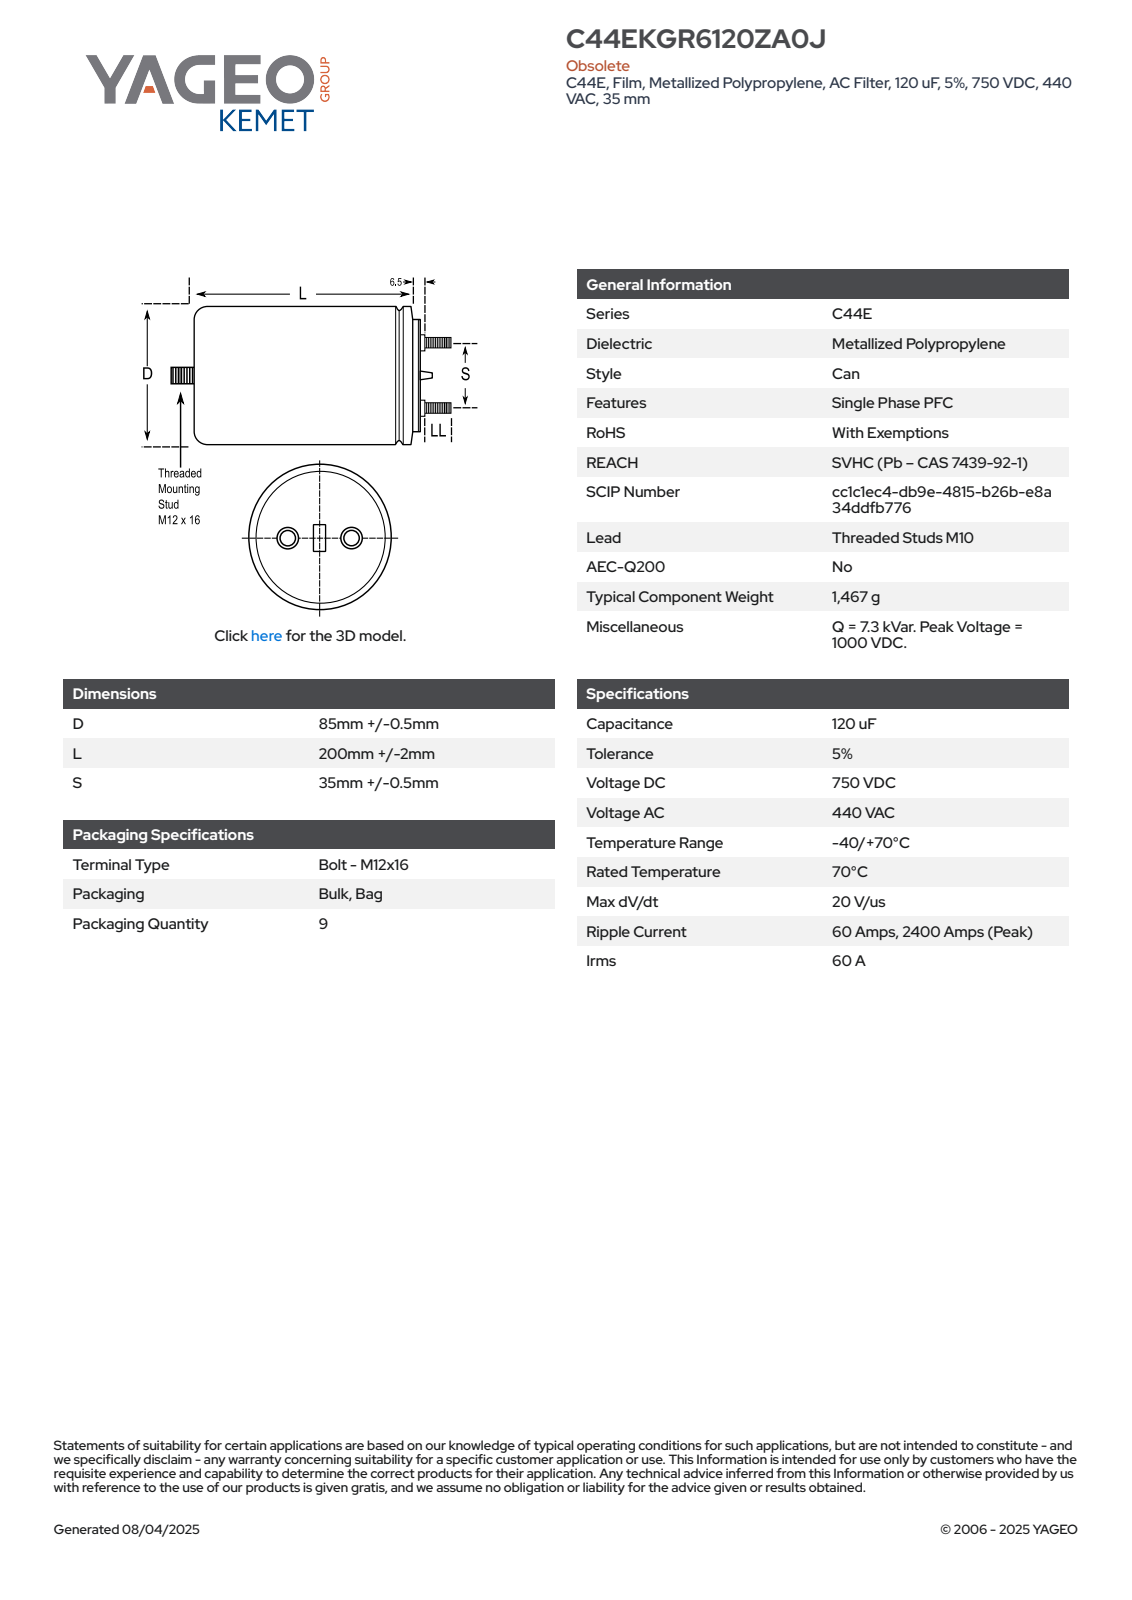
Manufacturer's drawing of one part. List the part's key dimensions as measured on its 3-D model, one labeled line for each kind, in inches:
Part name (STEP PRODUCT): CFP_C44E_85X200_D85.5L202S35.5LL25
STEP written by: SolidWorks 2014 (AUTOMOTIVE_DESIGN)
Units: inches
Bodies: 1 solid, 103 faces (34 planar, 34 cylindrical, 35 other)
Overall size (bounding box): 9.823 × 3.367 × 3.366
Volume: 72.01 in³ · Surface area: 109.1 in²
Round bosses / shafts (diameter × count): ⌀0.591 ×2, ⌀0.394 ×2, ⌀3.366 ×1, ⌀2.677 ×1, ⌀0.472 ×1
Partial cylindrical surfaces — rounded edges, fillets, slot ends (radius × count): R1.683 ×1
Main face-to-face distances: 8.11, 7.953, 0.157, 8.209, 0.256, 0.098, 8.386, 0.433, 0.276, 0.177
